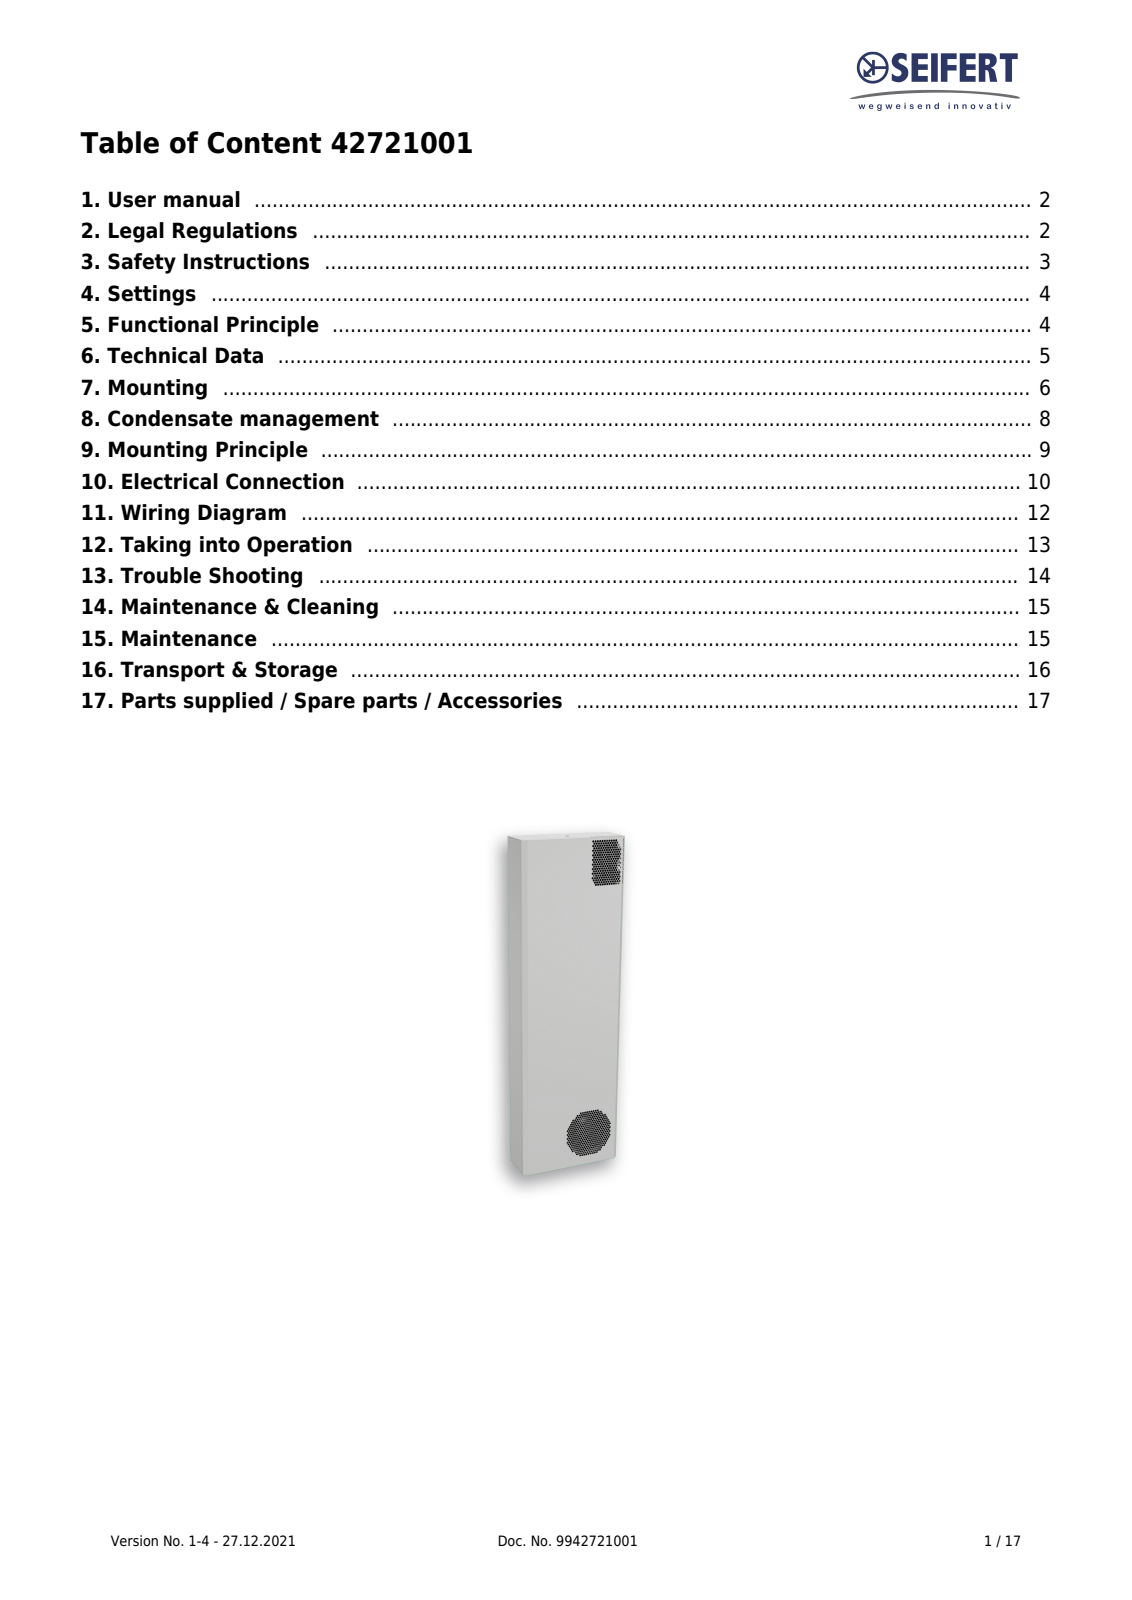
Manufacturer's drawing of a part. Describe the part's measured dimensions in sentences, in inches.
The part is named "4272SDX". Its 3-D file was written by "SolidWorks 2021 (AUTOMOTIVE_DESIGN)". It is 95 solids with 4045 faces: 2401 planar, 1224 cylindrical and 420 other. Overall it measures 52.551 by 15.551 by 6.417 inches. Its volume is 95.73 cubic inches and its surface area 4 738 square inches. Round holes: 684 of diameter 0.315, 43 of diameter 0.169, 21 of diameter 0.197, 19 of diameter 0.236, 14 of diameter 0.118, 10 of diameter 0.138, 9 of diameter 0.059, 9 of diameter 0.165, 4 of diameter 0.098, 4 of diameter 0.157, 2 of diameter 0.126, 2 of diameter 0.177. Round bosses or shafts: 20 of diameter 0.394, 19 of diameter 0.402, 19 of diameter 0.35, 9 of diameter 0.11, 6 of diameter 0.157, 5 of diameter 0.232, 5 of diameter 0.157, 4 of diameter 0.331. Partial cylindrical surfaces (rounded edges, fillets, slot ends): 60 of radius 0.02, 48 of radius 0.006, 26 of radius 0.031, 22 of radius 0.071, 15 of radius 0.039, 11 of radius 0.079, 10 of radius 0.059, 9 of radius 0.118. The main face-to-face distances are 0.039, 5.669, 5.709, 5.63, 15.512, 15.551, 15.472, 4.685, 0.984, 0.945. The hole center spacings are 0.361, 0.354, 0.618, 0.709, 0.94, 1.063, 1.28, 0.63.
